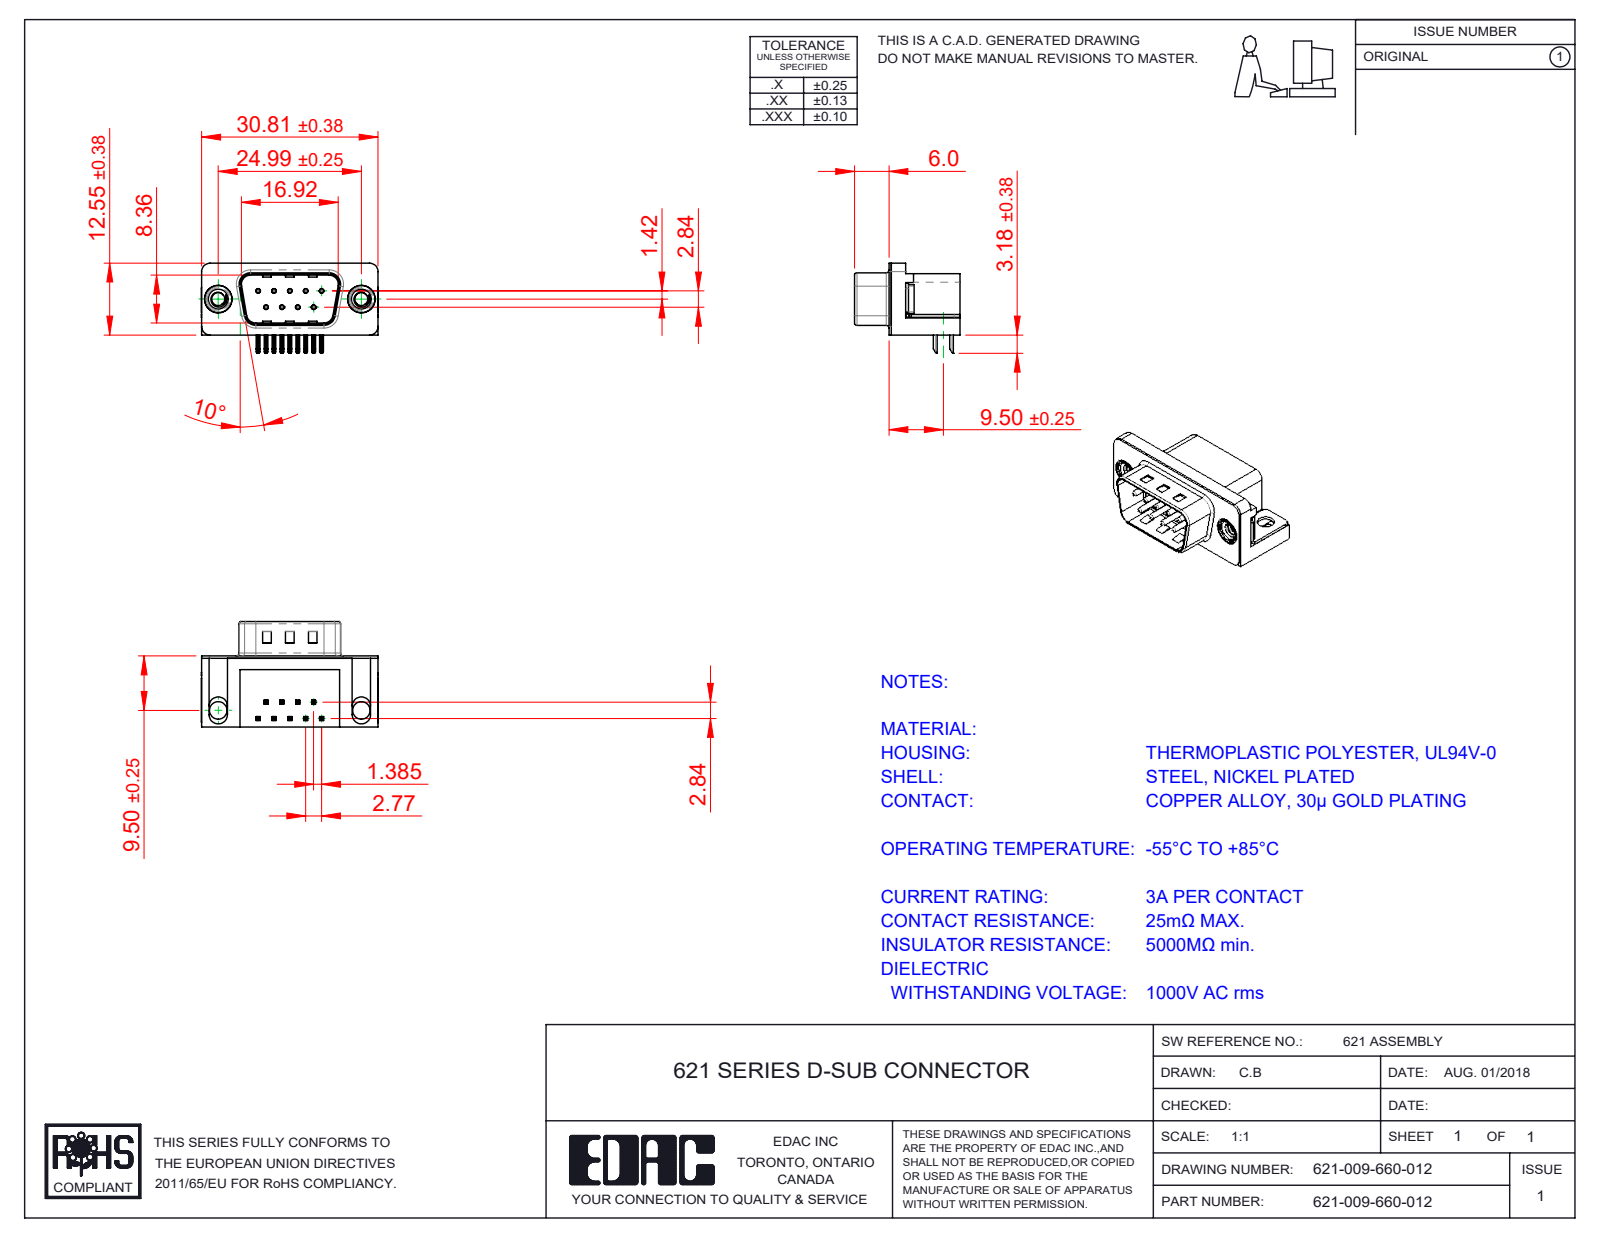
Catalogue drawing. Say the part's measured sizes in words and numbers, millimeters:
The part is named "621 Shell_9 Socket; 621 Contact Top; 621 4-40 Threaded Rivet; 621 Thru Hole Board Mount (+3 more)". Its 3-D file was written by "SolidWorks 2016 (CONFIG_CONTROL_DESIGN)". It is 15 solids with 989 faces: 571 planar, 315 cylindrical and 103 other. Overall it measures 30.89 by 18.4 by 15.73 millimeters. Its volume is 3 245 cubic millimeters and its surface area 4 408 square millimeters. Round holes: 9 of diameter 0.35, 9 of diameter 0.8, 2 of diameter 2.26, 2 of diameter 3.05, 2 of diameter 4, 2 of diameter 4.8, 2 of diameter 5. Round bosses or shafts: 9 of diameter 0.75, 2 of diameter 4.9, 2 of diameter 4.75, 2 of diameter 3.9. Partial cylindrical surfaces (rounded edges, fillets, slot ends): 44 of radius 0.25, 18 of radius 0.12, 16 of radius 1, 9 of radius 0.5, 8 of radius 1.5, 8 of radius 1.6, 4 of radius 0.9, 4 of radius 2. The main face-to-face distances are 0.4, 12, 12.4, 10.35, 0.5, 2.9, 9.5, 2.5, 2.1, 0.35. The hole center spacings are 3.16, 2.77, 5.54, 5.03, 5.04, 8.31, 7.48, 7.49.
